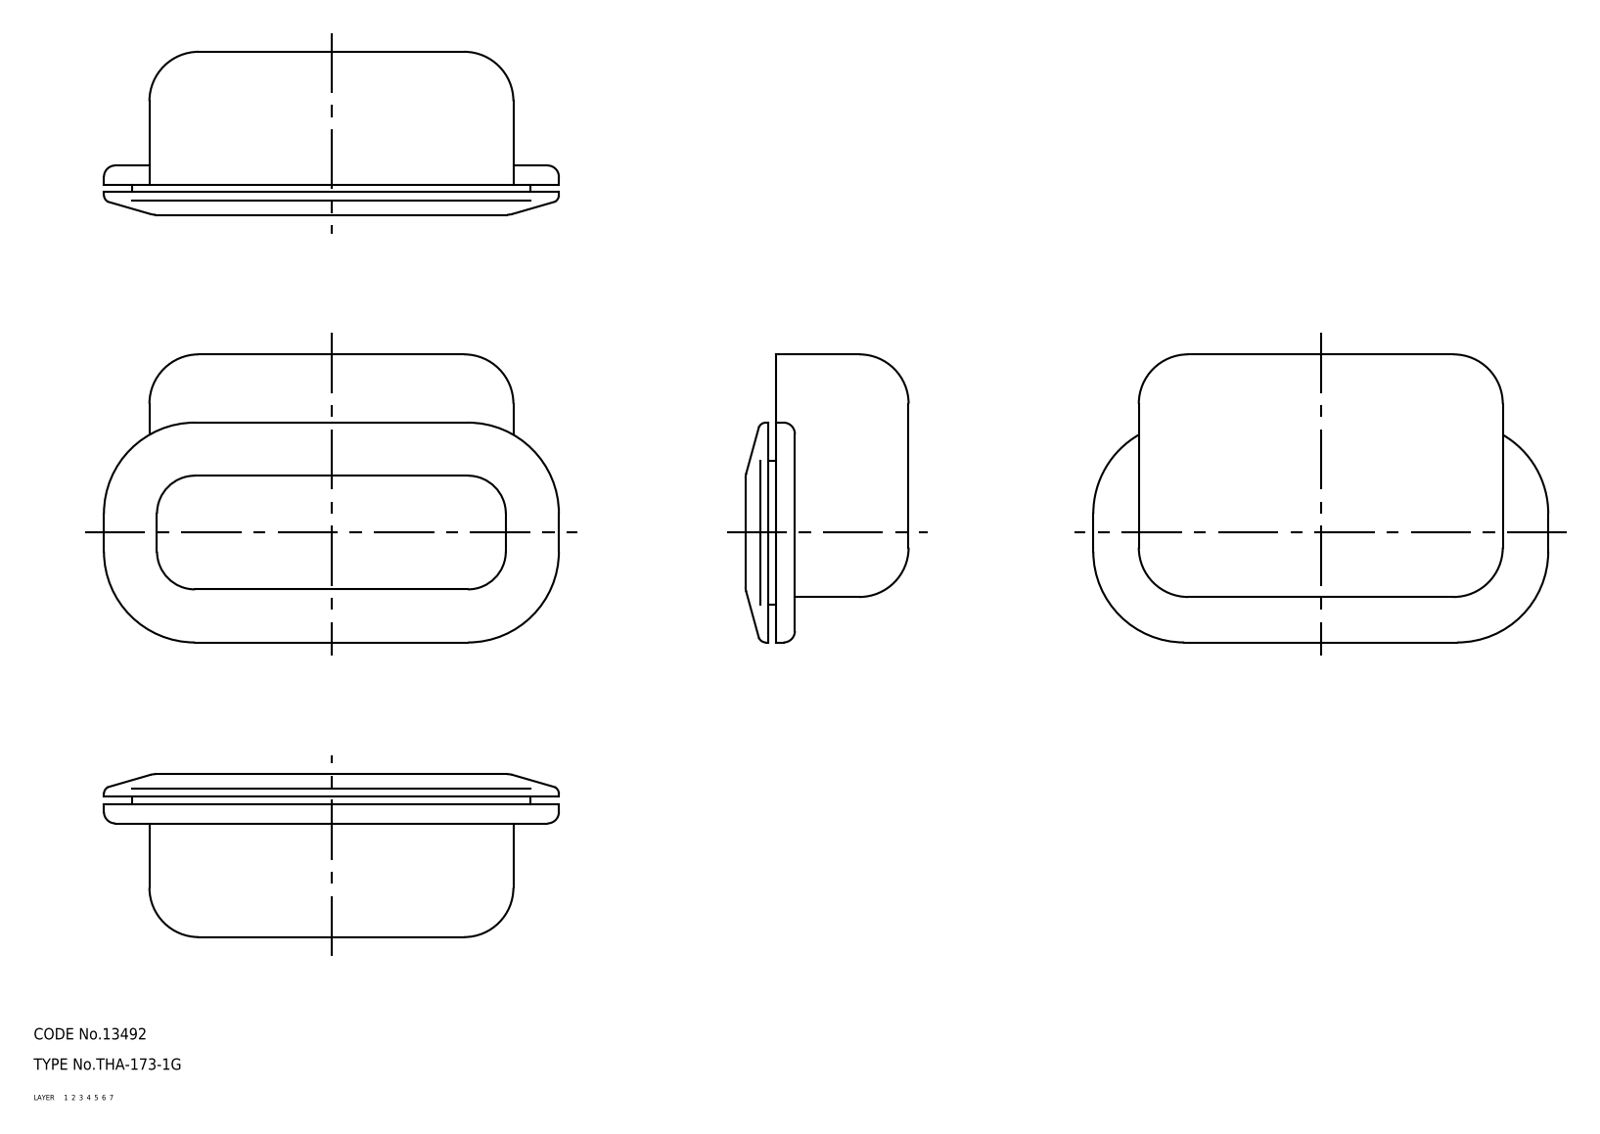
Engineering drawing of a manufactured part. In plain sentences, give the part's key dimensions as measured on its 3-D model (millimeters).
The part is named "pull". Its 3-D file was written by "CADfix (AUTOMOTIVE_DESIGN)". It is 1 solid with 105 faces: 0 planar, 0 cylindrical and 105 other. Overall it measures 120 by 76 by 43 millimeters. Its volume is 66 085 cubic millimeters and its surface area 46 983 square millimeters.
